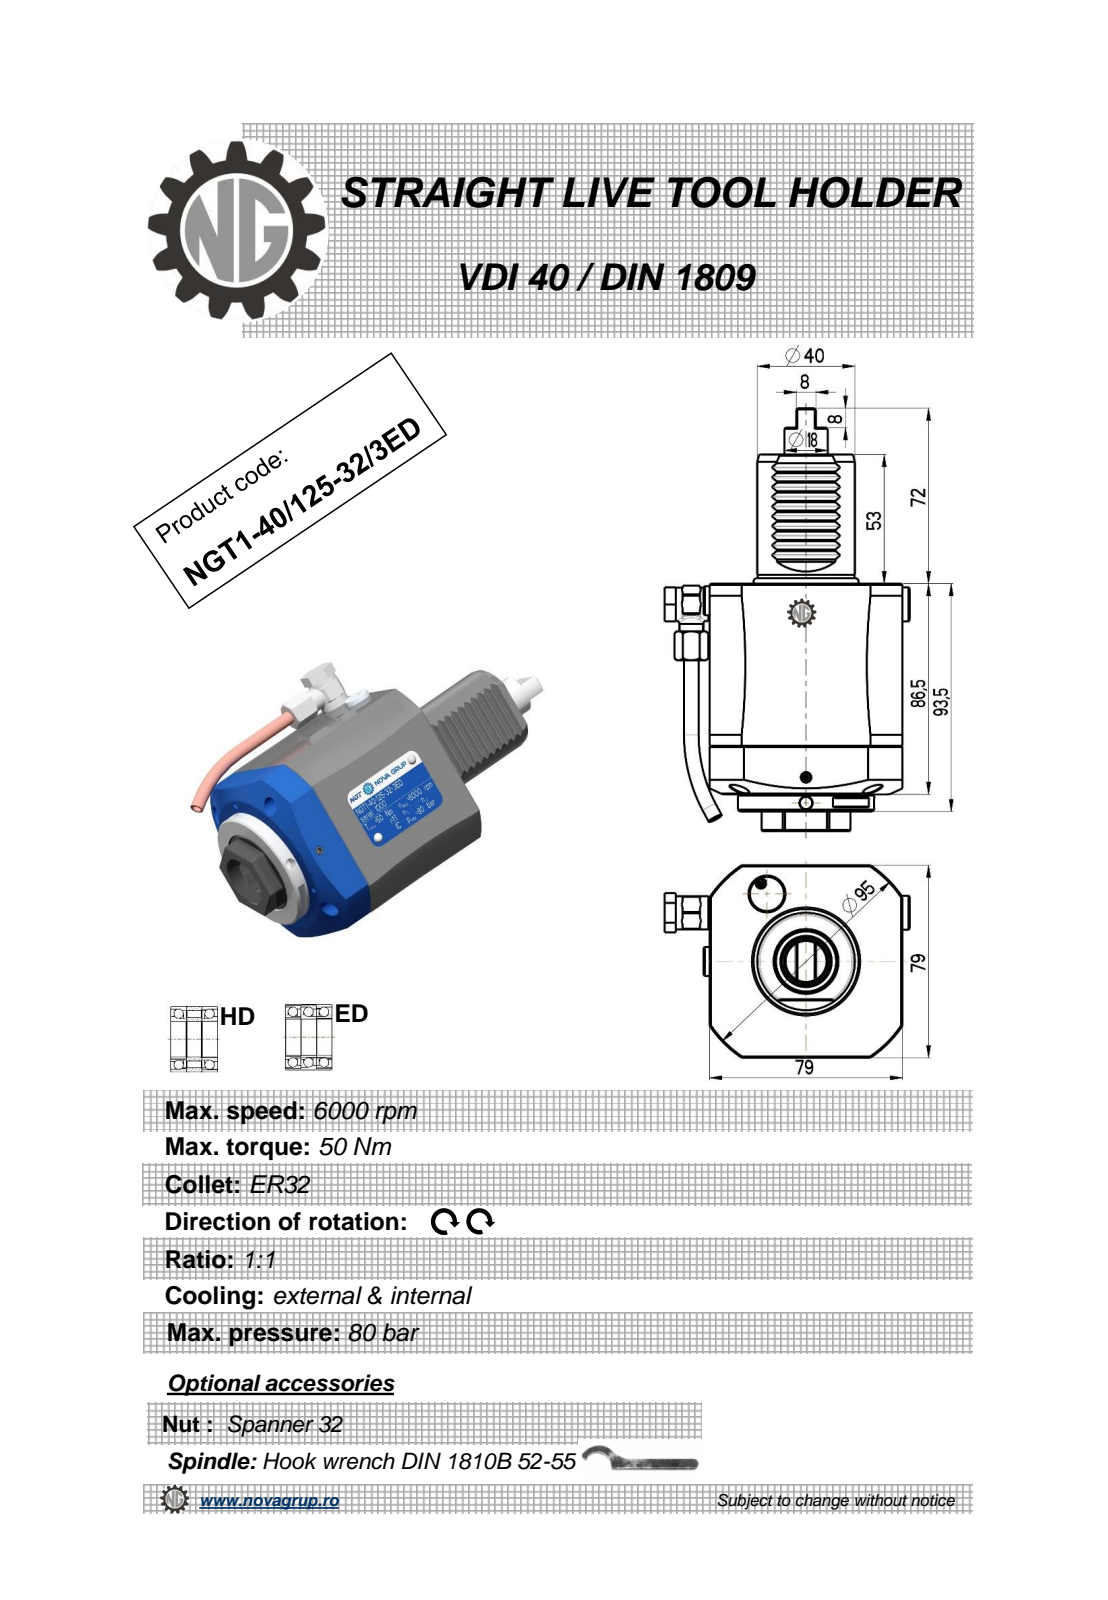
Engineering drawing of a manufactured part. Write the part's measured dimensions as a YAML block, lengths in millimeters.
part_name: "NGT1_40_125_32_3HD"
step_written_by: "PRO/ENGINEER BY PARAMETRIC TECHNOLOGY CORPORATION, 2010280 (CONFIG_CONTROL_DESIGN)"
units: millimeters
bodies: {solids: 2, faces: 372, planar: 154, cylindrical: 99, other: 119}
overall_size: [173.5, 100.4, 79]
volume: 592837
surface_area: 53443
round_holes:
  - {diameter: 4, count: 3}
  - {diameter: 5, count: 2}
  - {diameter: 3, count: 1}
  - {diameter: 6, count: 1}
  - {diameter: 6.2, count: 1}
  - {diameter: 9, count: 1}
  - {diameter: 10, count: 1}
  - {diameter: 11, count: 1}
  - {diameter: 23, count: 1}
round_bosses_or_shafts:
  - {diameter: 56, count: 1}
  - {diameter: 40, count: 1}
  - {diameter: 17.8, count: 1}
  - {diameter: 14, count: 1}
  - {diameter: 13.6, count: 1}
  - {diameter: 13, count: 1}
  - {diameter: 12, count: 1}
  - {diameter: 10, count: 1}
partial_cylinders:
  - {radius: 0.3, count: 10}
  - {radius: 0.41, count: 6}
  - {radius: 0.5, count: 4}
  - {radius: 0.8, count: 2}
  - {radius: 7.7, count: 1}
  - {radius: 47, count: 1}
  - {radius: 47.5, count: 1}
face_to_face_distances: [79, 86.5, 7, 93.5, 146.5, 139.5, 53, 2.83, 8, 8.48]
hole_center_spacings: [0.4, 51.08, 51.45, 83.92]
